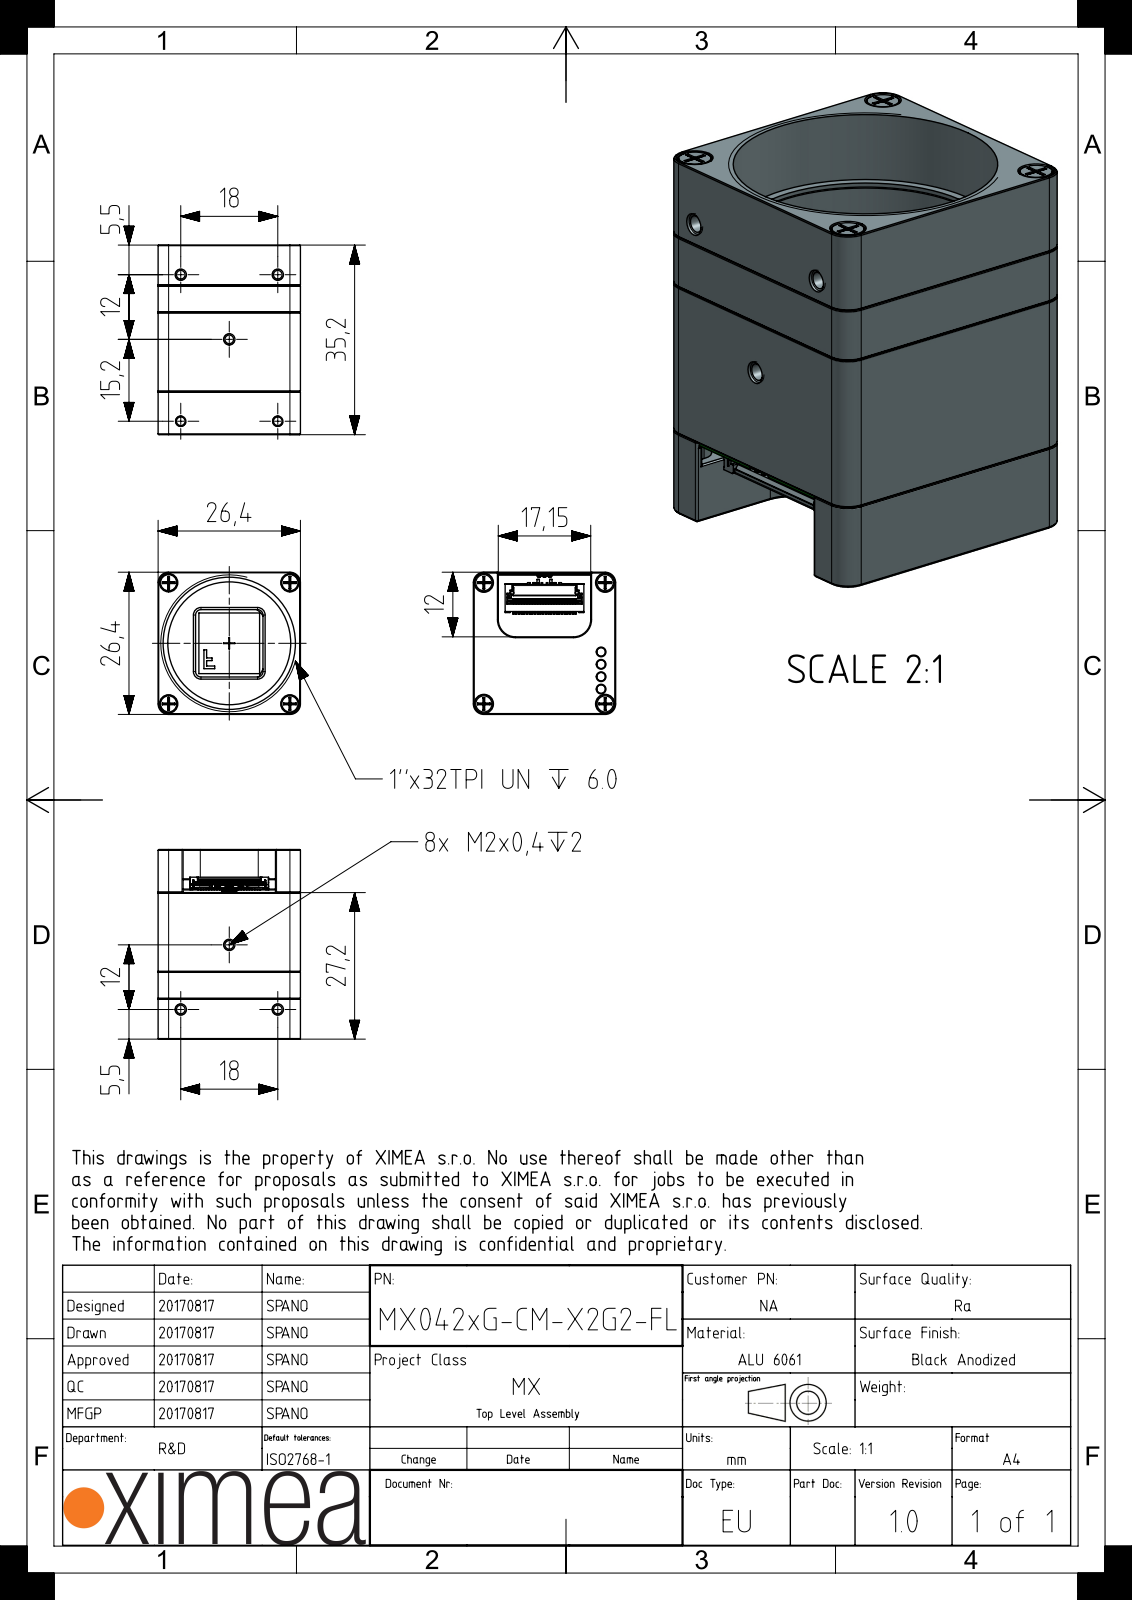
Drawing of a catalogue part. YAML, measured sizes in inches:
part_name: "CMV4000_Glass; CMV4000_Package; ANDON-96UPGA-Socket; MECH-O-RING-22X1-VI370 (+8 more)"
step_written_by: "SIEMENS PLM Software NX 1907 (AUTOMOTIVE_DESIGN)"
units: inches
bodies: {solids: 405, faces: 12070, planar: 7238, cylindrical: 3538, other: 1294}
overall_size: [1.386, 1.039, 1.039]
volume: 0.73
surface_area: 35.53
round_holes:
  - {diameter: 0.02, count: 95}
  - {diameter: 0.03, count: 95}
  - {diameter: 0.063, count: 13}
  - {diameter: 0.035, count: 4}
  - {diameter: 0.071, count: 4}
  - {diameter: 0.079, count: 4}
  - {diameter: 0.083, count: 4}
  - {diameter: 0.118, count: 4}
  - {diameter: 0.126, count: 4}
  - {diameter: 0.132, count: 4}
  - {diameter: 0.055, count: 1}
  - {diameter: 0.073, count: 1}
round_bosses_or_shafts:
  - {diameter: 0.012, count: 95}
  - {diameter: 0.075, count: 4}
  - {diameter: 0.064, count: 4}
  - {diameter: 0.033, count: 4}
  - {diameter: 0.118, count: 2}
  - {diameter: 0.063, count: 2}
  - {diameter: 0.984, count: 1}
  - {diameter: 0.85, count: 1}
partial_cylinders:
  - {radius: 0.006, count: 82}
  - {radius: 0.004, count: 34}
  - {radius: 0.039, count: 20}
  - {radius: 0.015, count: 18}
  - {radius: 0.013, count: 17}
  - {radius: 0.059, count: 17}
  - {radius: 0.051, count: 16}
  - {radius: 0.008, count: 14}
face_to_face_distances: [0.039, 1.039, 0.142, 0.437, 0.181, 0.319, 0.177, 0.622, 0.441, 0.583]
hole_center_spacings: [0.112, 0.25, 0.158, 0.206, 0.224, 0.269, 0.354, 0.18]
